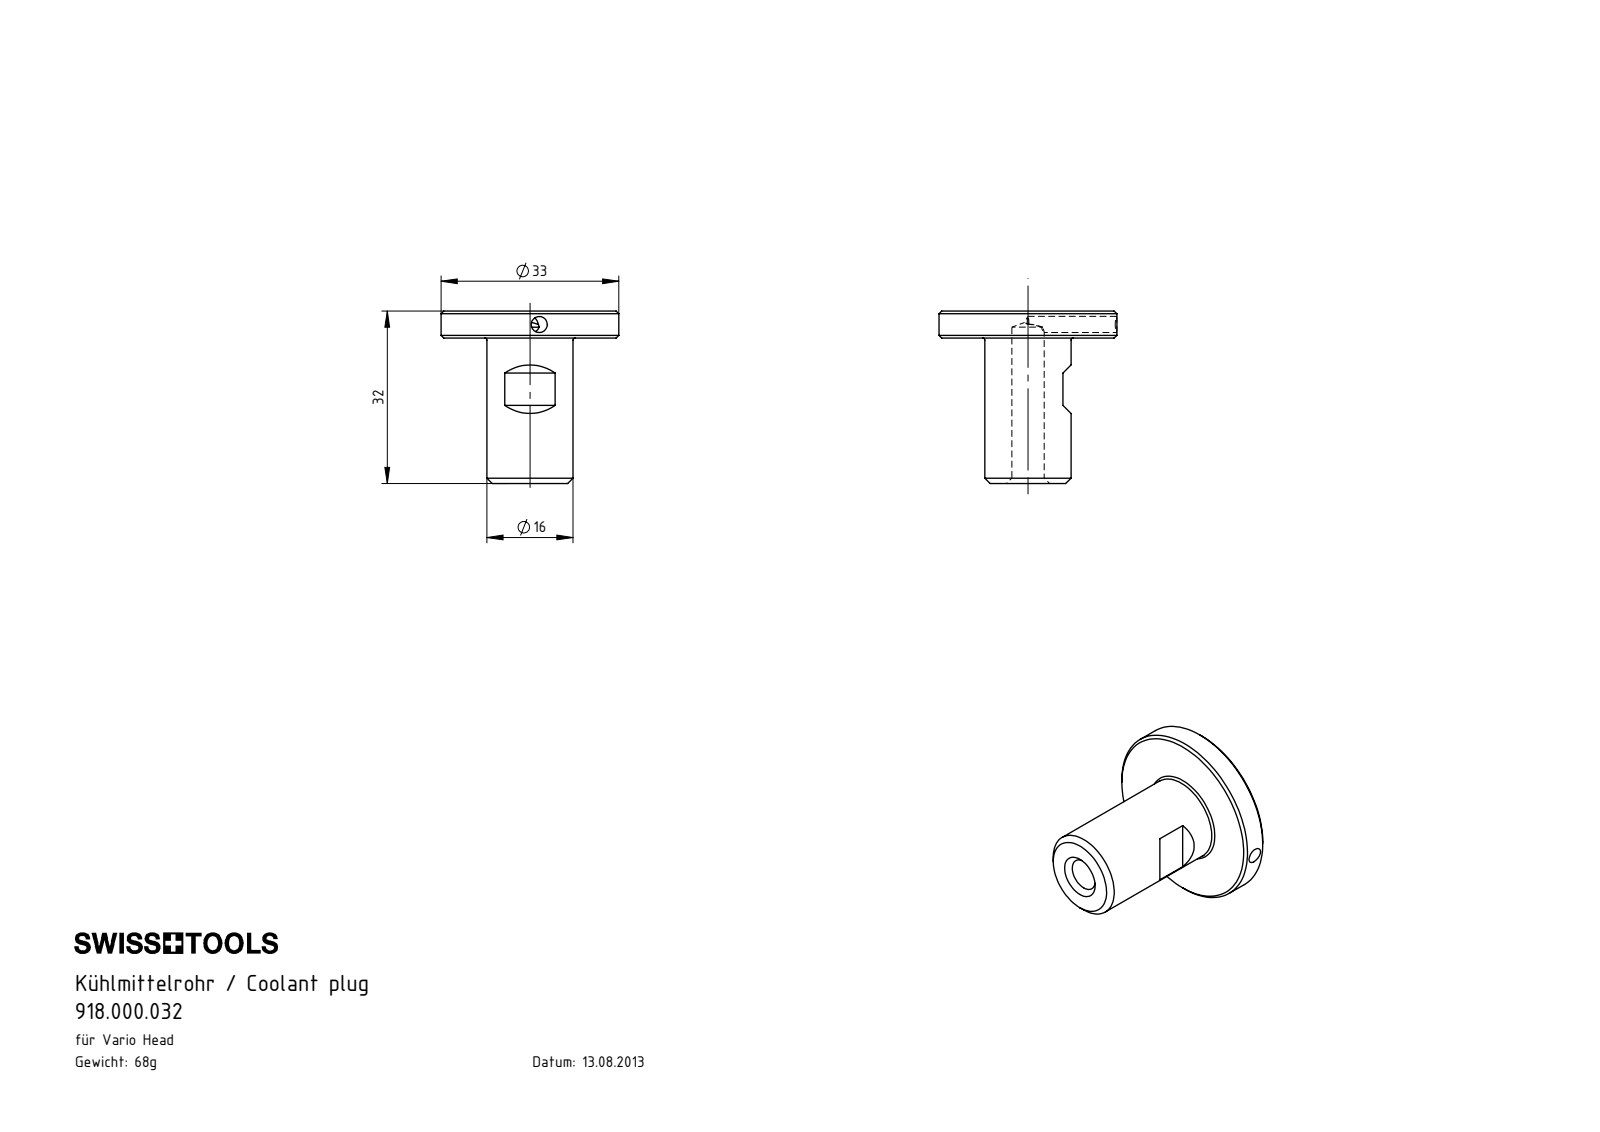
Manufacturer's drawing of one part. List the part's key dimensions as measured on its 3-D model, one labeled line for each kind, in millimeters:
Part name (STEP PRODUCT): 918.000.032
STEP written by: SolidWorks 2022 (AUTOMOTIVE_DESIGN)
Units: millimetres
Bodies: 1 solid, 28 faces (6 planar, 8 cylindrical, 14 other)
Overall size (bounding box): 33 × 33 × 32
Volume: 8 641 mm³ · Surface area: 4 154 mm²
Round holes (diameter × count): ⌀3 ×1, ⌀6 ×1
Round bosses / shafts (diameter × count): ⌀33 ×1, ⌀16 ×1
Main face-to-face distances: 5, 27, 32
